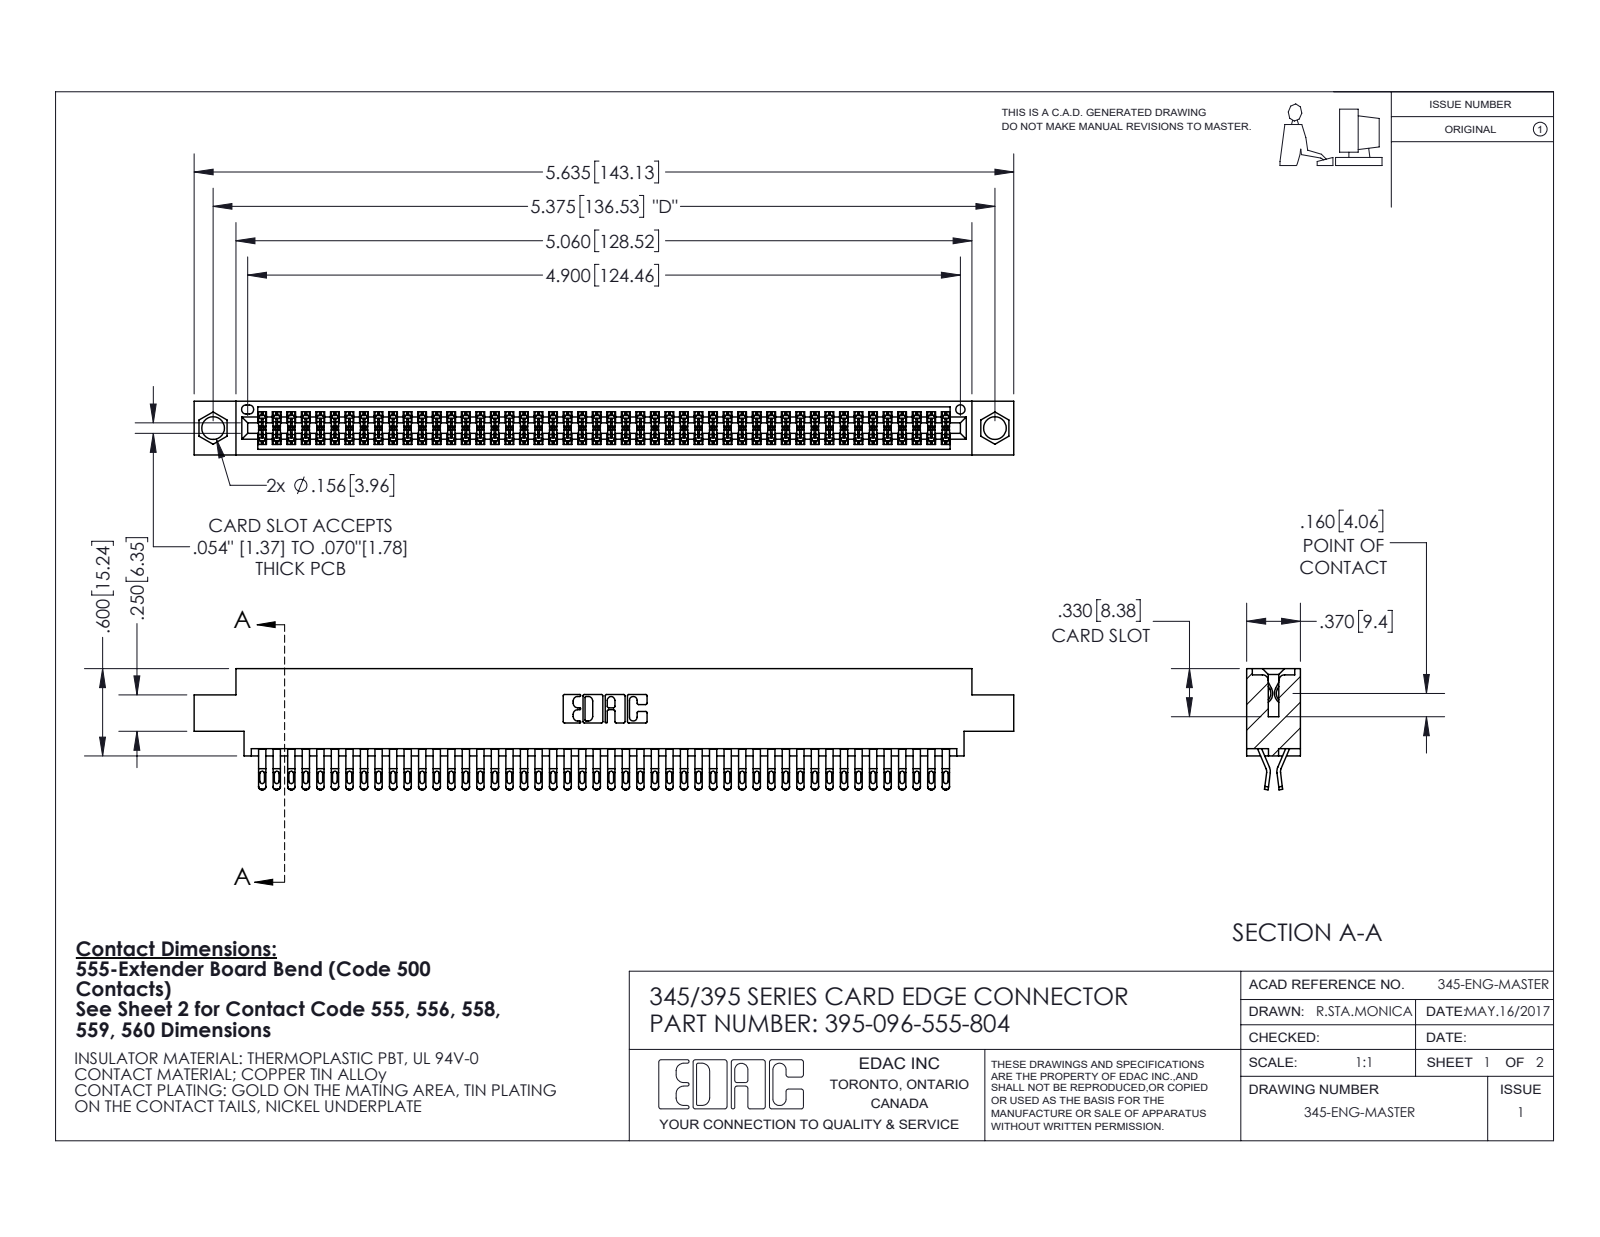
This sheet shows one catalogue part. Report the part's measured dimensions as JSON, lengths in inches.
{"part_name": "395-096-555-804; 345 Part_0.170 Offset - 0.156 Dia-TI; 345-292-001_555 Tail", "step_written_by": "SolidWorks 2020 (CONFIG_CONTROL_DESIGN)", "units": "inches", "bodies": {"solids": 97, "faces": 5520, "planar": 3074, "cylindrical": 2446, "other": 0}, "overall_size": [5.635, 0.832, 0.37], "volume_in3": 0.855, "surface_area_in2": 33.79, "round_holes": [[0.156, 2], [0.064, 1]], "partial_cylinders_radius": [[0.016, 240], [0.006, 192], [0.02, 192], [0.01, 22], [0.007, 6], [0.031, 6], [0.026, 3], [0.01, 2]], "face_to_face_distances": [0.072, 0.298, 0.37, 0.025, 0.2, 0.098, 0.272, 0.225, 0.175, 0.149], "hole_center_spacings": [0.27, 5.139, 5.375]}
